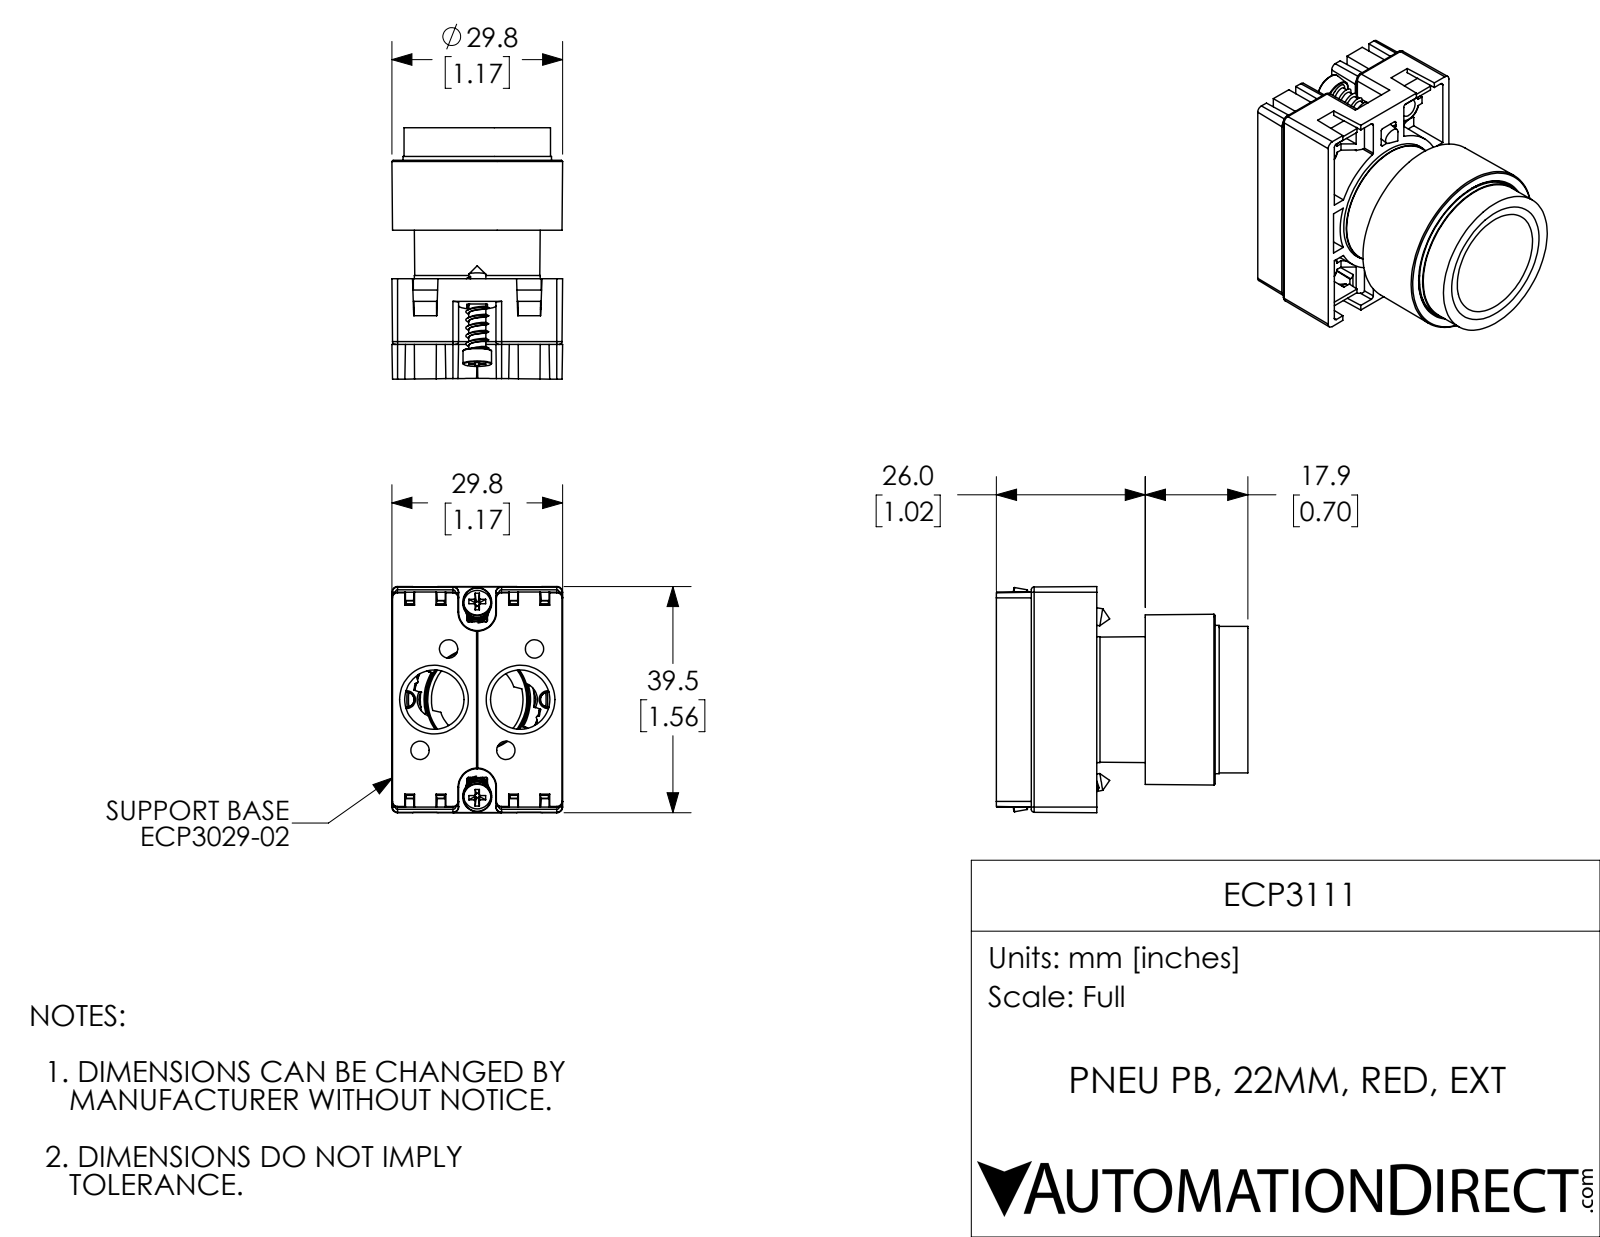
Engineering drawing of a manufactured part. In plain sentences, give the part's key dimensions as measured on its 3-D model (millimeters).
The part is named "ECP3111". Its 3-D file was written by "SolidWorks 2017 (AUTOMOTIVE_DESIGN)". It is 7 solids with 781 faces: 364 planar, 133 cylindrical and 284 other. Overall it measures 43.9 by 39.5 by 29.8 millimeters. Its volume is 16 800 cubic millimeters and its surface area 19 080 square millimeters. Round holes: 4 of diameter 2.1, 2 of diameter 10.3, 1 of diameter 17.7, 1 of diameter 18.6. Round bosses or shafts: 2 of diameter 5, 2 of diameter 3, 1 of diameter 25.9, 1 of diameter 25.6, 1 of diameter 22. Partial cylindrical surfaces (rounded edges, fillets, slot ends): 18 of radius 0.5, 8 of radius 0.2, 8 of radius 0.3, 4 of radius 0.2, 4 of radius 1, 2 of radius 0.2, 2 of radius 3, 2 of radius 3.3. The main face-to-face distances are 32, 4.5, 1.7, 18.2, 24.4, 20.6, 11.5, 14.9, 13.4, 13.2. The hole center spacings are 7.7, 13.7, 20.8, 7.5, 12, 24.7, 27.5, 15.
